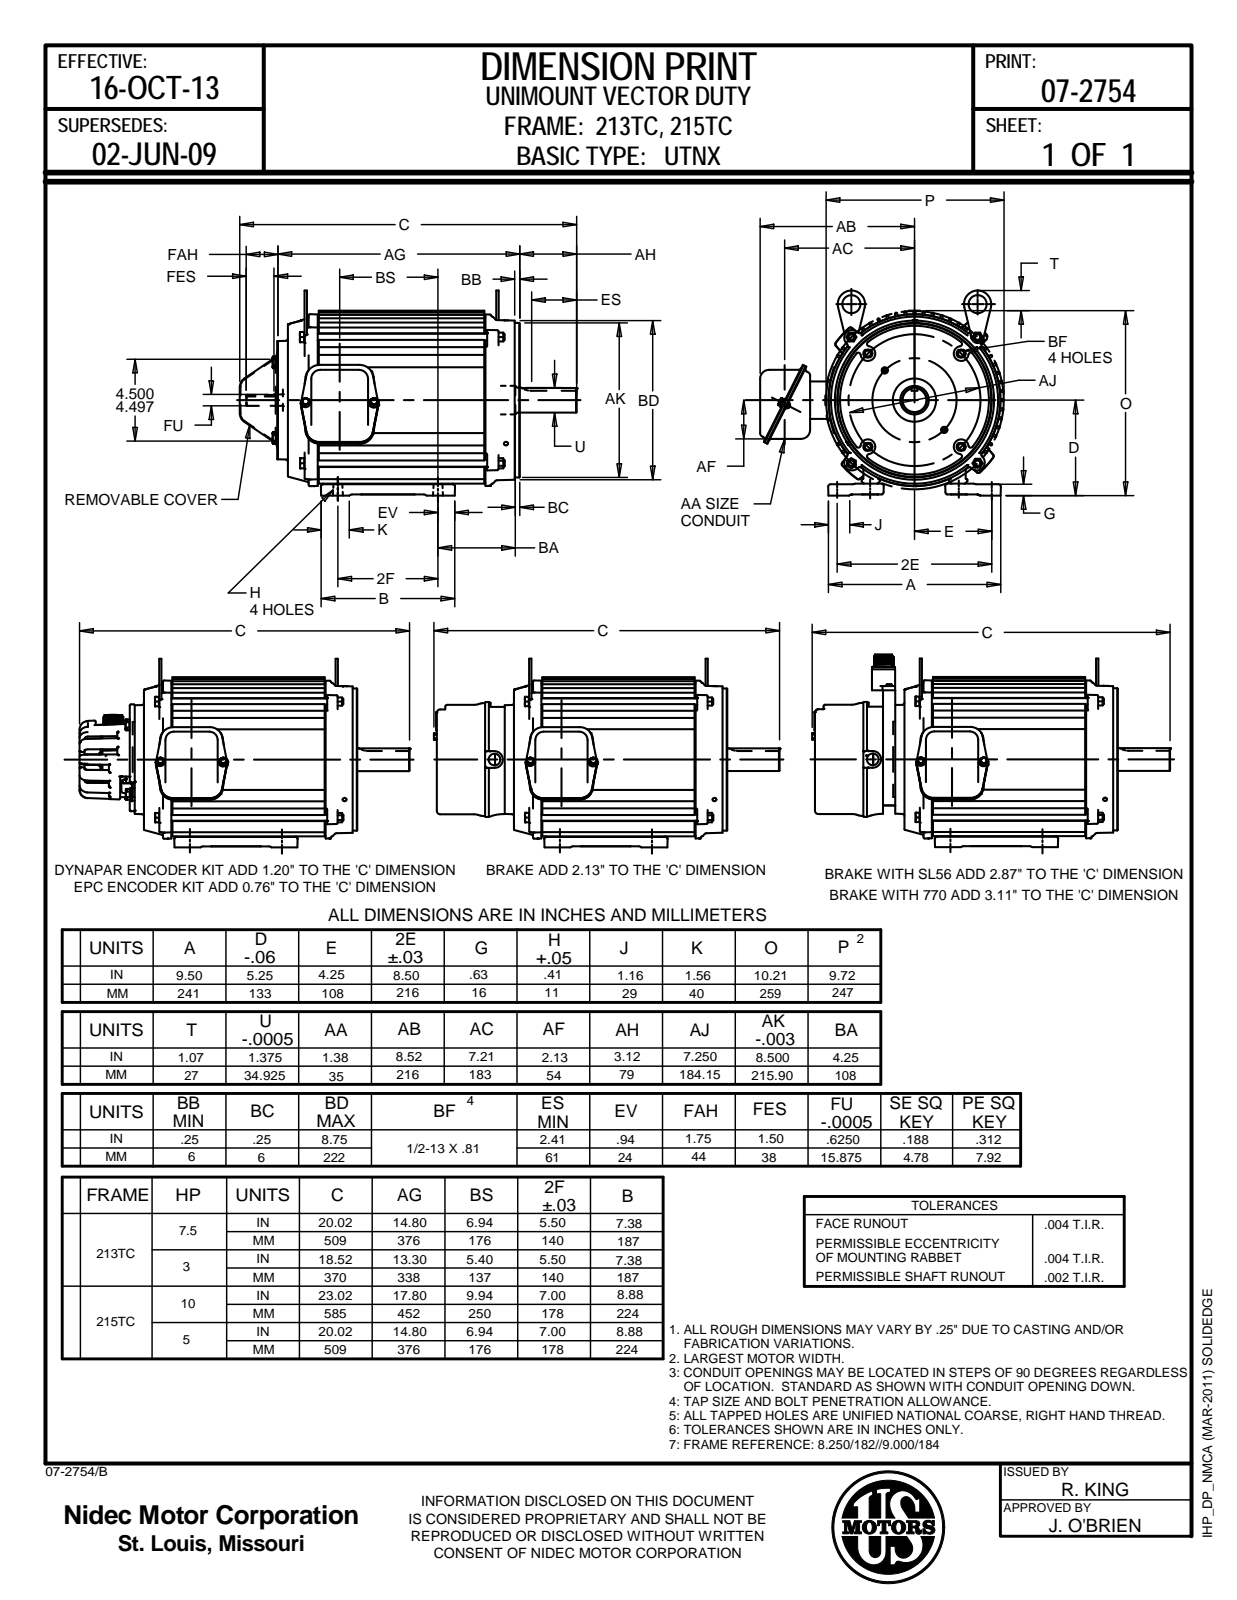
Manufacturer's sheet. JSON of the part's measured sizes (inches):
{"part_name": "UN5T3BC", "step_written_by": "SolidWorks 2021 (AUTOMOTIVE_DESIGN)", "units": "inches", "bodies": {"solids": 5, "faces": 2258, "planar": 417, "cylindrical": 700, "other": 1141}, "overall_size": [20.115, 13.226, 11.325], "volume_in3": 1075, "surface_area_in2": 1131, "round_holes": [[0.313, 4], [0.328, 4], [0.406, 4], [0.436, 4], [0.107, 2], [0.227, 2], [0.281, 2], [0.391, 2], [1, 2], [0.173, 1], [1.191, 1], [1.38, 1]], "round_bosses_or_shafts": [[0.323, 2], [9.866, 1], [9.131, 1], [8.5, 1], [6.5, 1], [4.5, 1], [1.573, 1], [1.375, 1]], "partial_cylinders_radius": [[0.125, 140], [0.063, 68], [0.06, 54], [0.1, 54], [0.25, 22], [0.031, 18], [0.5, 18], [0.118, 16]], "face_to_face_distances": [13.613, 0.9, 14.513, 0.822, 0.078, 13.691, 0.315, 0.585, 0.237, 13.928], "hole_center_spacings": [4.666, 5.719, 6.1, 6.939, 0.688, 1.281, 1.969, 2.317]}
